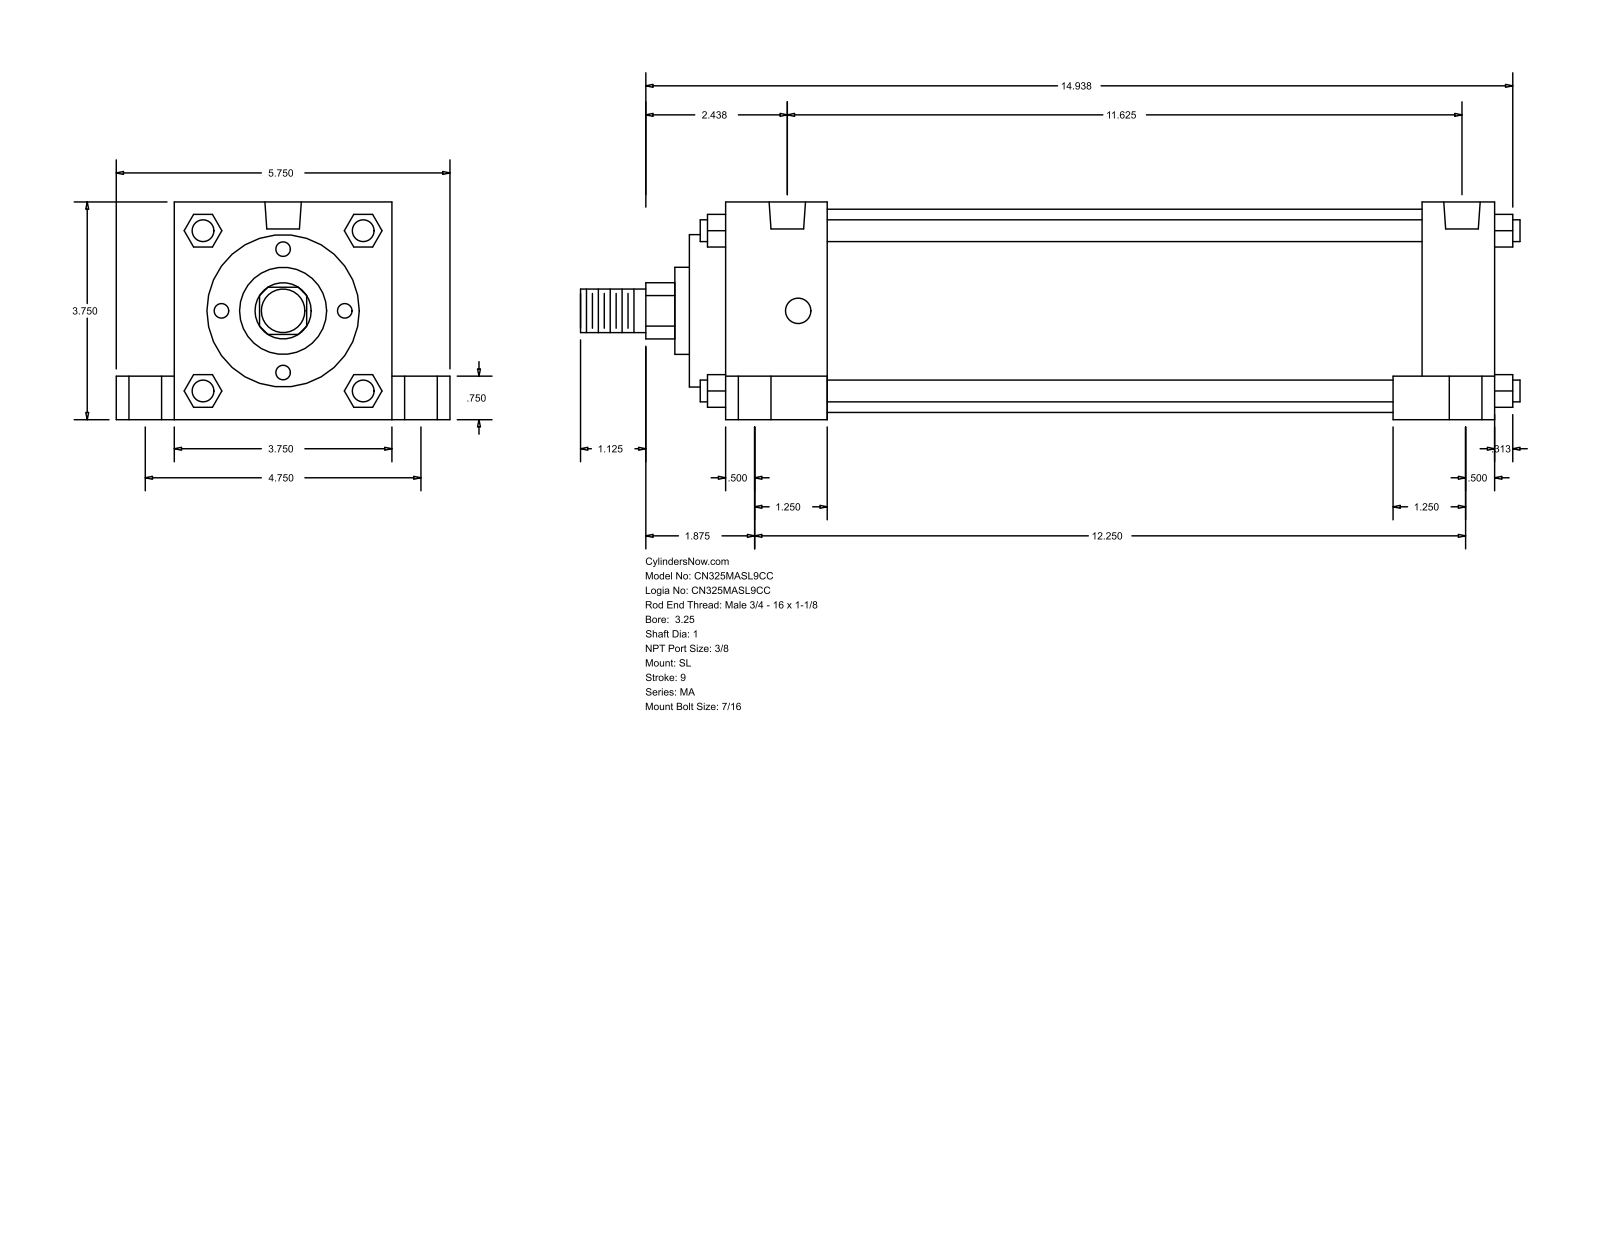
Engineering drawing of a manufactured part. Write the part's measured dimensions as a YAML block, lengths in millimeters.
part_name: "MA_SL__0325_1"
step_written_by: "GSSL Pune (CONFIG_CONTROL_DESIGN)"
units: millimeters
bodies: {solids: 0, faces: 150, planar: 113, cylindrical: 37, other: 0}
overall_size: [411.16, 146.05, 95.25]
round_holes:
  - {diameter: 11.11, count: 4}
  - {diameter: 14.29, count: 4}
  - {diameter: 20.64, count: 4}
  - {diameter: 15.93, count: 2}
round_bosses_or_shafts:
  - {diameter: 9.53, count: 4}
  - {diameter: 88.9, count: 1}
  - {diameter: 66.67, count: 1}
  - {diameter: 38.1, count: 1}
  - {diameter: 25.4, count: 1}
  - {diameter: 19.05, count: 1}
partial_cylinders:
  - {radius: 12.29, count: 1}
face_to_face_distances: [95.24, 336.56, 260.35, 15.87, 25.41, 120.65, 19.05, 304.81, 31.75, 44.46]
hole_center_spacings: [4.76, 60.35, 60.66, 62, 63.27, 120.66, 285.76, 290.52]
